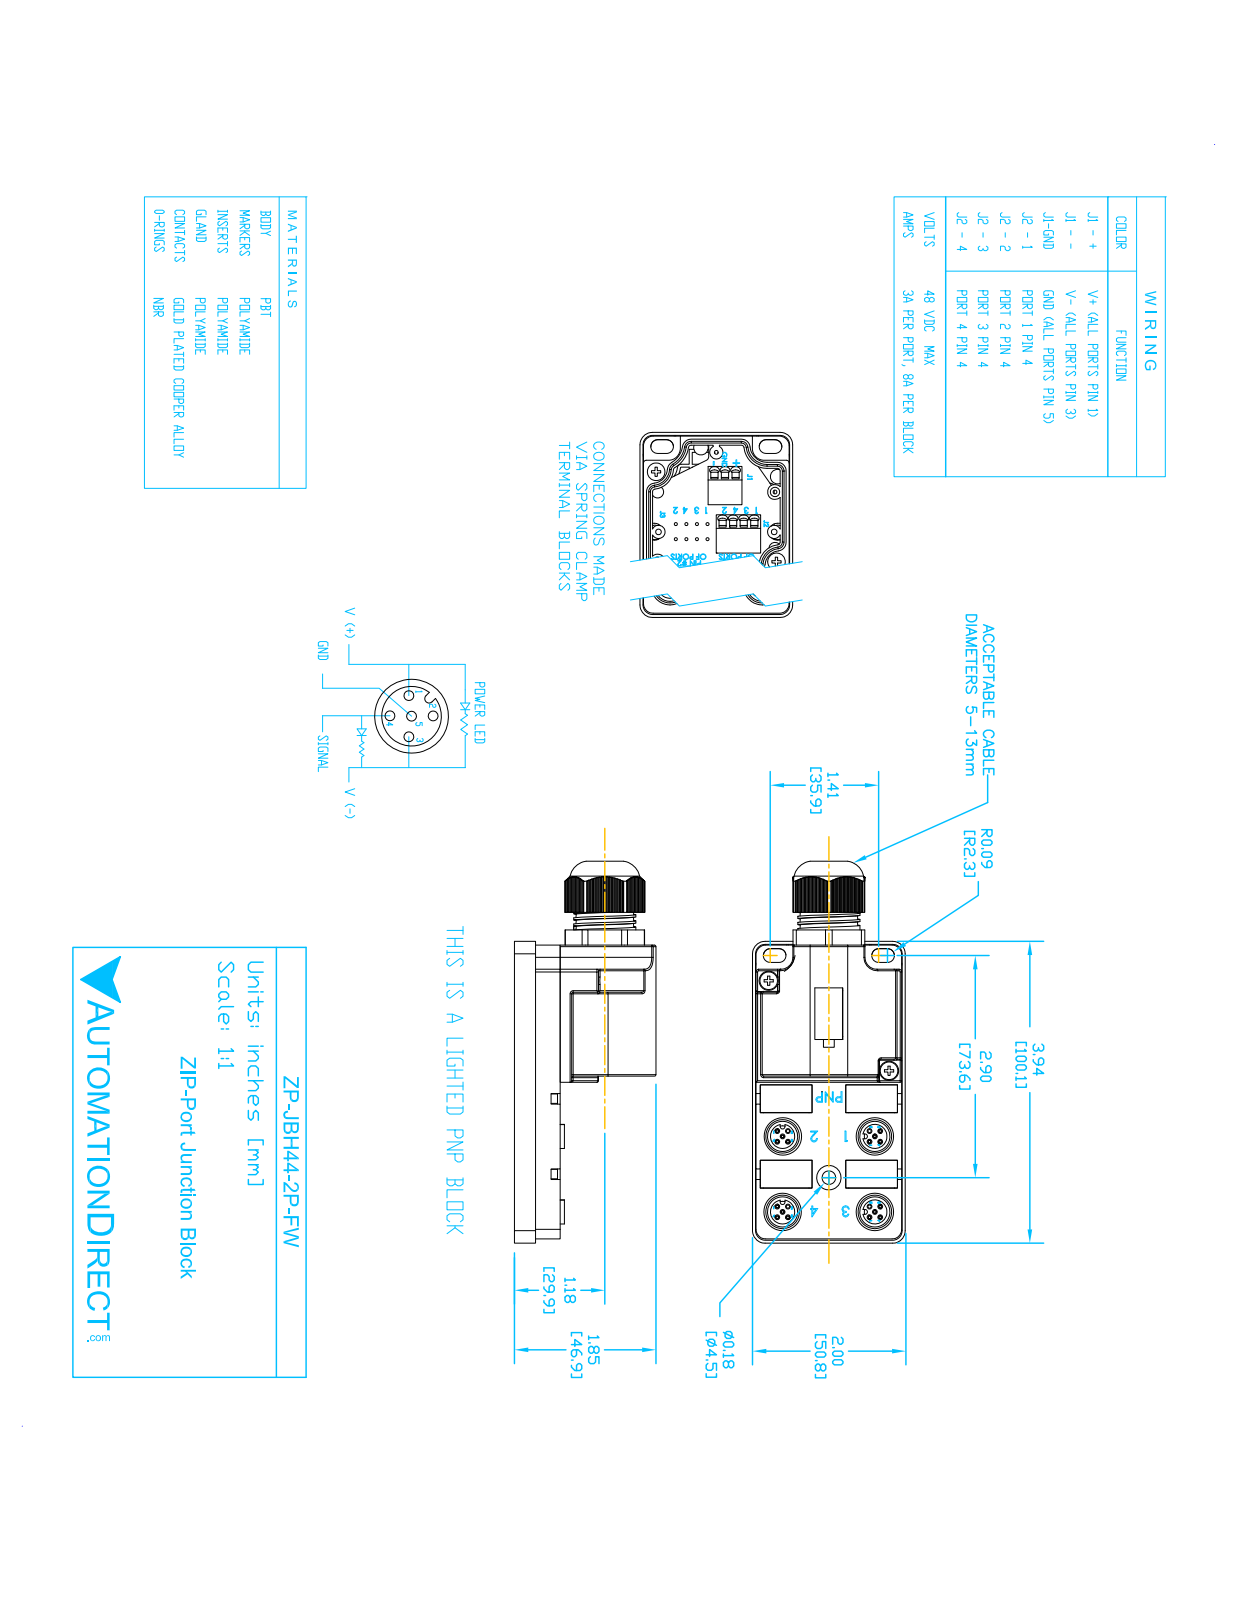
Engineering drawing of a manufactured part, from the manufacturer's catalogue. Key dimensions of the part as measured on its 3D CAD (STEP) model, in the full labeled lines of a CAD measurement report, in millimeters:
Part name (STEP PRODUCT): ZP-JBH44-00-FW
STEP written by: SolidWorks 2017 (AUTOMOTIVE_DESIGN)
Units: millimetres
Bodies: 7 solids, 1065 faces (636 planar, 267 cylindrical, 162 other)
Overall size (bounding box): 126.6 × 50.6 × 46.9
Volume: 131 600 mm³ · Surface area: 29 060 mm²
Round holes (diameter × count): ⌀1.1 ×20, ⌀1.6 ×20, ⌀11.1 ×4, ⌀12.4 ×4, ⌀6.4 ×2, ⌀6.6 ×1, ⌀8.1 ×1, ⌀9.4 ×1, ⌀12.4 ×1, ⌀15.2 ×1
Round bosses / shafts (diameter × count): ⌀8 ×3, ⌀20.6 ×1, ⌀20 ×1, ⌀8 ×1
Partial cylindrical surfaces — rounded edges, fillets, slot ends (radius × count): R0.5 ×34, R2.3 ×8, R0.8 ×4, R4.2 ×4, R7.9 ×4, R0.9 ×2, R3.2 ×2, R4 ×2
Main face-to-face distances: 15.1, 43.4, 48.3, 1, 0.9, 14.1, 3.2, 47.4, 1.2, 49.4
Hole centre spacings: 2.5, 3.5, 30.6, 23.3, 28.9, 30.8, 32.4, 25
